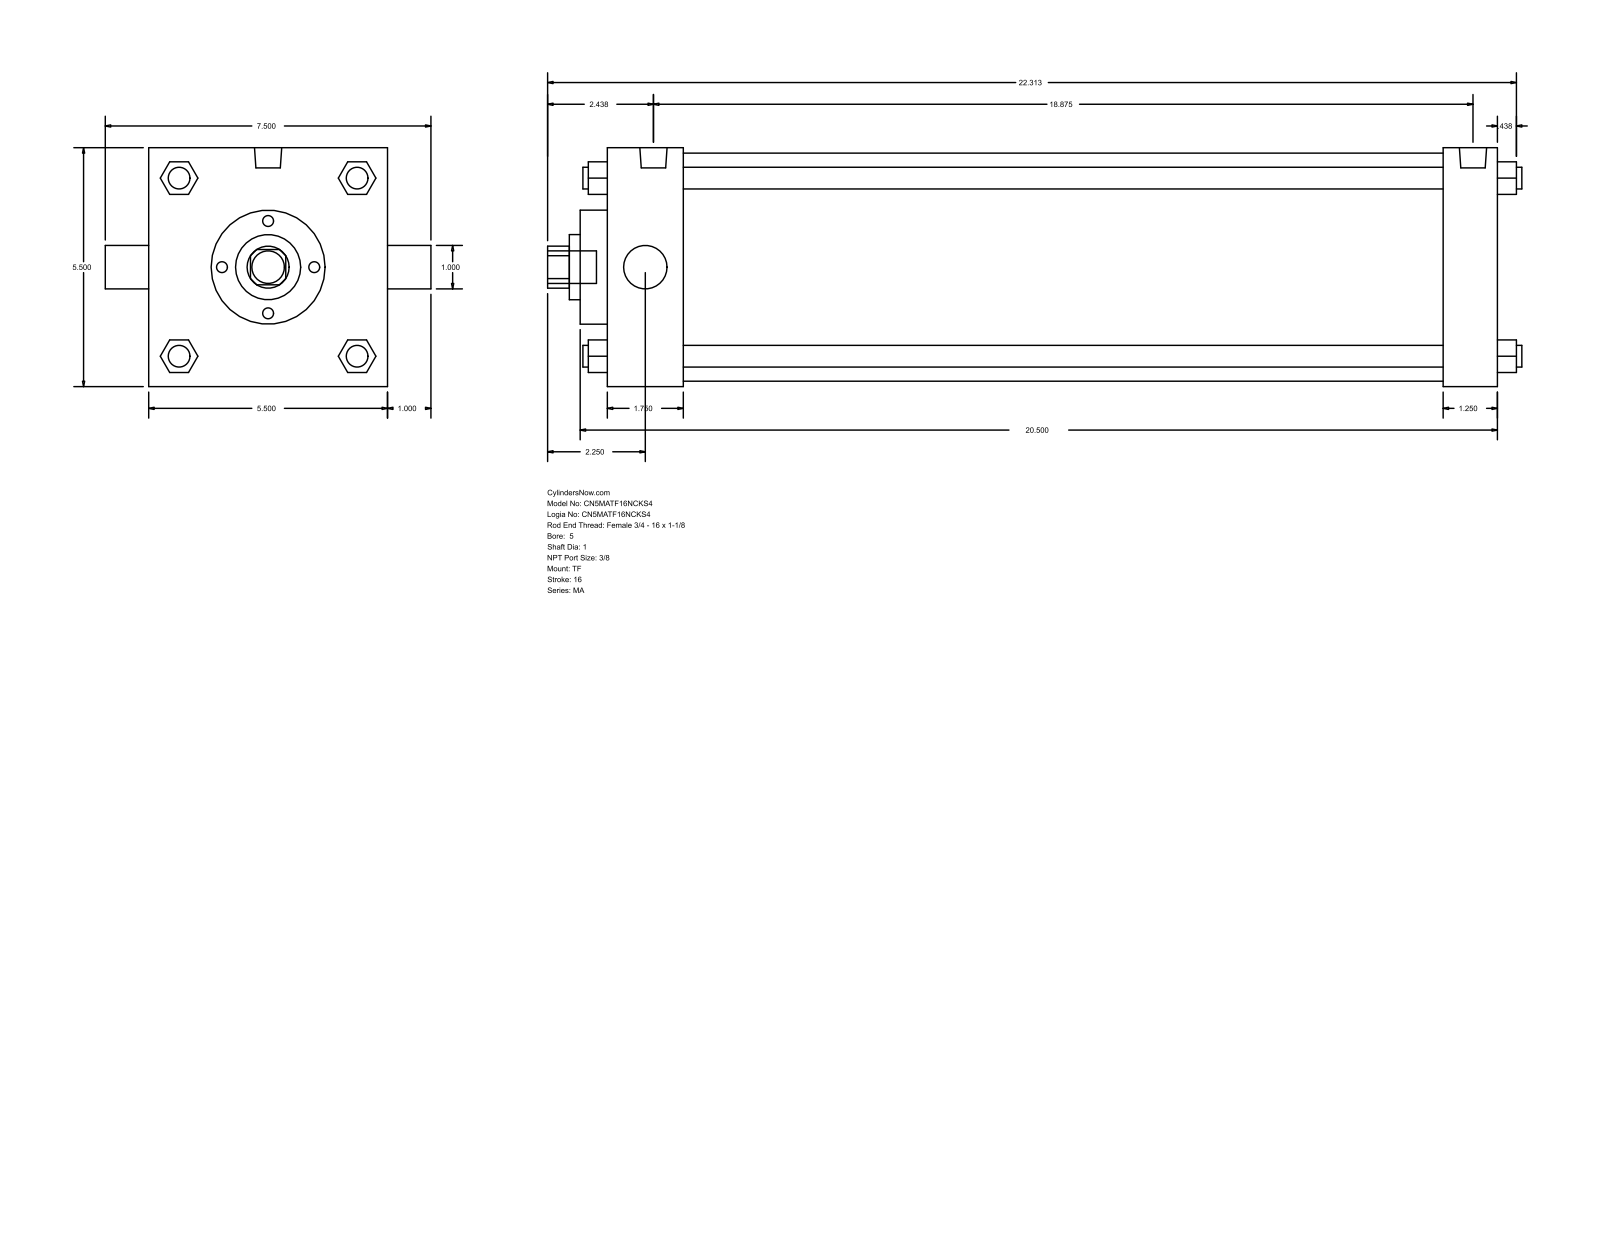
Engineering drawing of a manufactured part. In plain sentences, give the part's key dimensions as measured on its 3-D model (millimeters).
The part is named "MA_TF__0500_1". Its 3-D file was written by "GSSL Pune (CONFIG_CONTROL_DESIGN)". It is 0 solids with 122 faces: 93 planar, 29 cylindrical and 0 other. Overall it measures 569.91 by 190.5 by 139.7 millimeters. Round holes: 2 of diameter 25.4, 1 of diameter 38.1, 1 of diameter 66.67, 1 of diameter 133.35. Round bosses or shafts: 4 of diameter 12.7, 3 of diameter 11.11, 2 of diameter 15.93, 1 of diameter 19.05. Partial cylindrical surfaces (rounded edges, fillets, slot ends): 1 of radius 12.29. The main face-to-face distances are 139.7, 520.7, 488.96, 31.74, 44.46, 444.5, 476.24, 15.87, 60.33, 504.83.
